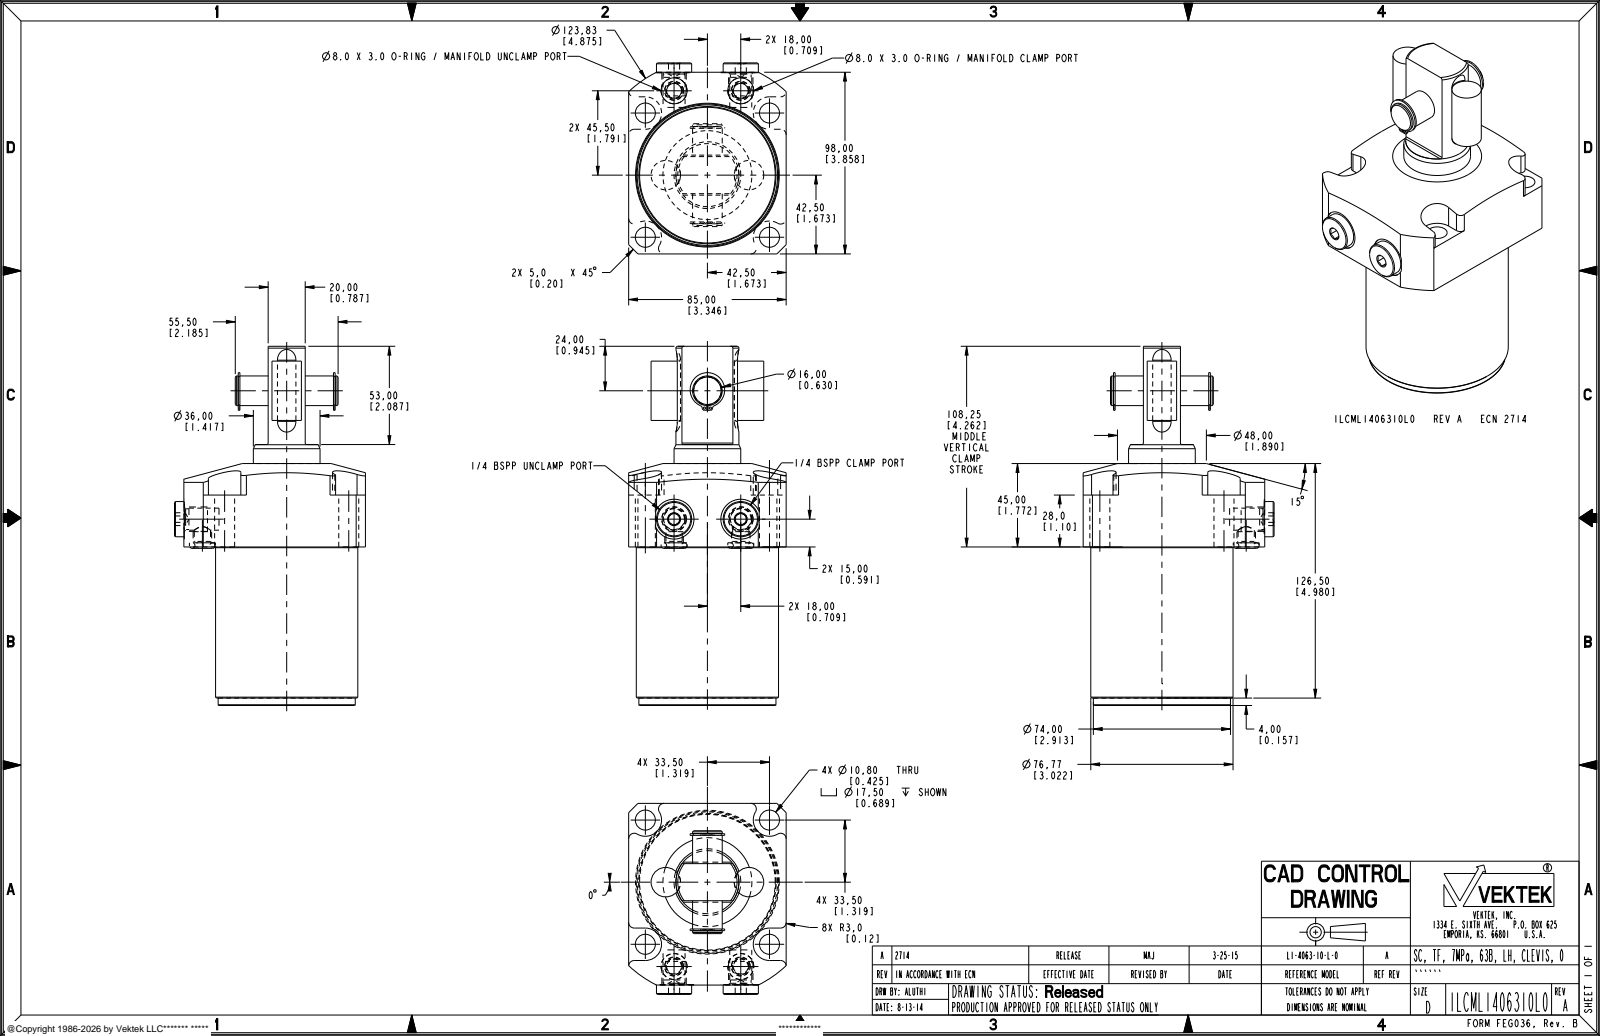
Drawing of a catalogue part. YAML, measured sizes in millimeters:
part_name: "ILCML1406310L0"
step_written_by: "PRO/ENGINEER BY PARAMETRIC TECHNOLOGY CORPORATION, 2013320 (AUTOMOTIVE_DESIGN)"
units: millimeters
bodies: {solids: 5, faces: 237, planar: 85, cylindrical: 104, other: 48}
overall_size: [193.75, 103.05, 85]
volume: 772538
surface_area: 71961
round_holes:
  - {diameter: 10.8, count: 4}
  - {diameter: 1.19, count: 2}
  - {diameter: 6, count: 2}
  - {diameter: 8.75, count: 2}
  - {diameter: 11.89, count: 2}
  - {diameter: 14, count: 2}
  - {diameter: 21.5, count: 2}
  - {diameter: 15.5, count: 1}
round_bosses_or_shafts:
  - {diameter: 19, count: 2}
  - {diameter: 15.88, count: 2}
  - {diameter: 13.16, count: 2}
  - {diameter: 11.2, count: 2}
  - {diameter: 10, count: 2}
  - {diameter: 76.77, count: 1}
  - {diameter: 74, count: 1}
  - {diameter: 36, count: 1}
partial_cylinders:
  - {radius: 3, count: 8}
  - {radius: 8.75, count: 4}
  - {radius: 0.8, count: 2}
  - {radius: 1.19, count: 2}
  - {radius: 1.34, count: 2}
  - {radius: 7.94, count: 2}
  - {radius: 61.91, count: 1}
face_to_face_distances: [85, 85.5, 98, 52.5, 32.5, 65.5, 20, 45.5, 45, 28]
hole_center_spacings: [67, 9.49, 19.6, 36, 52.88, 62.1, 63.03, 71.55]
